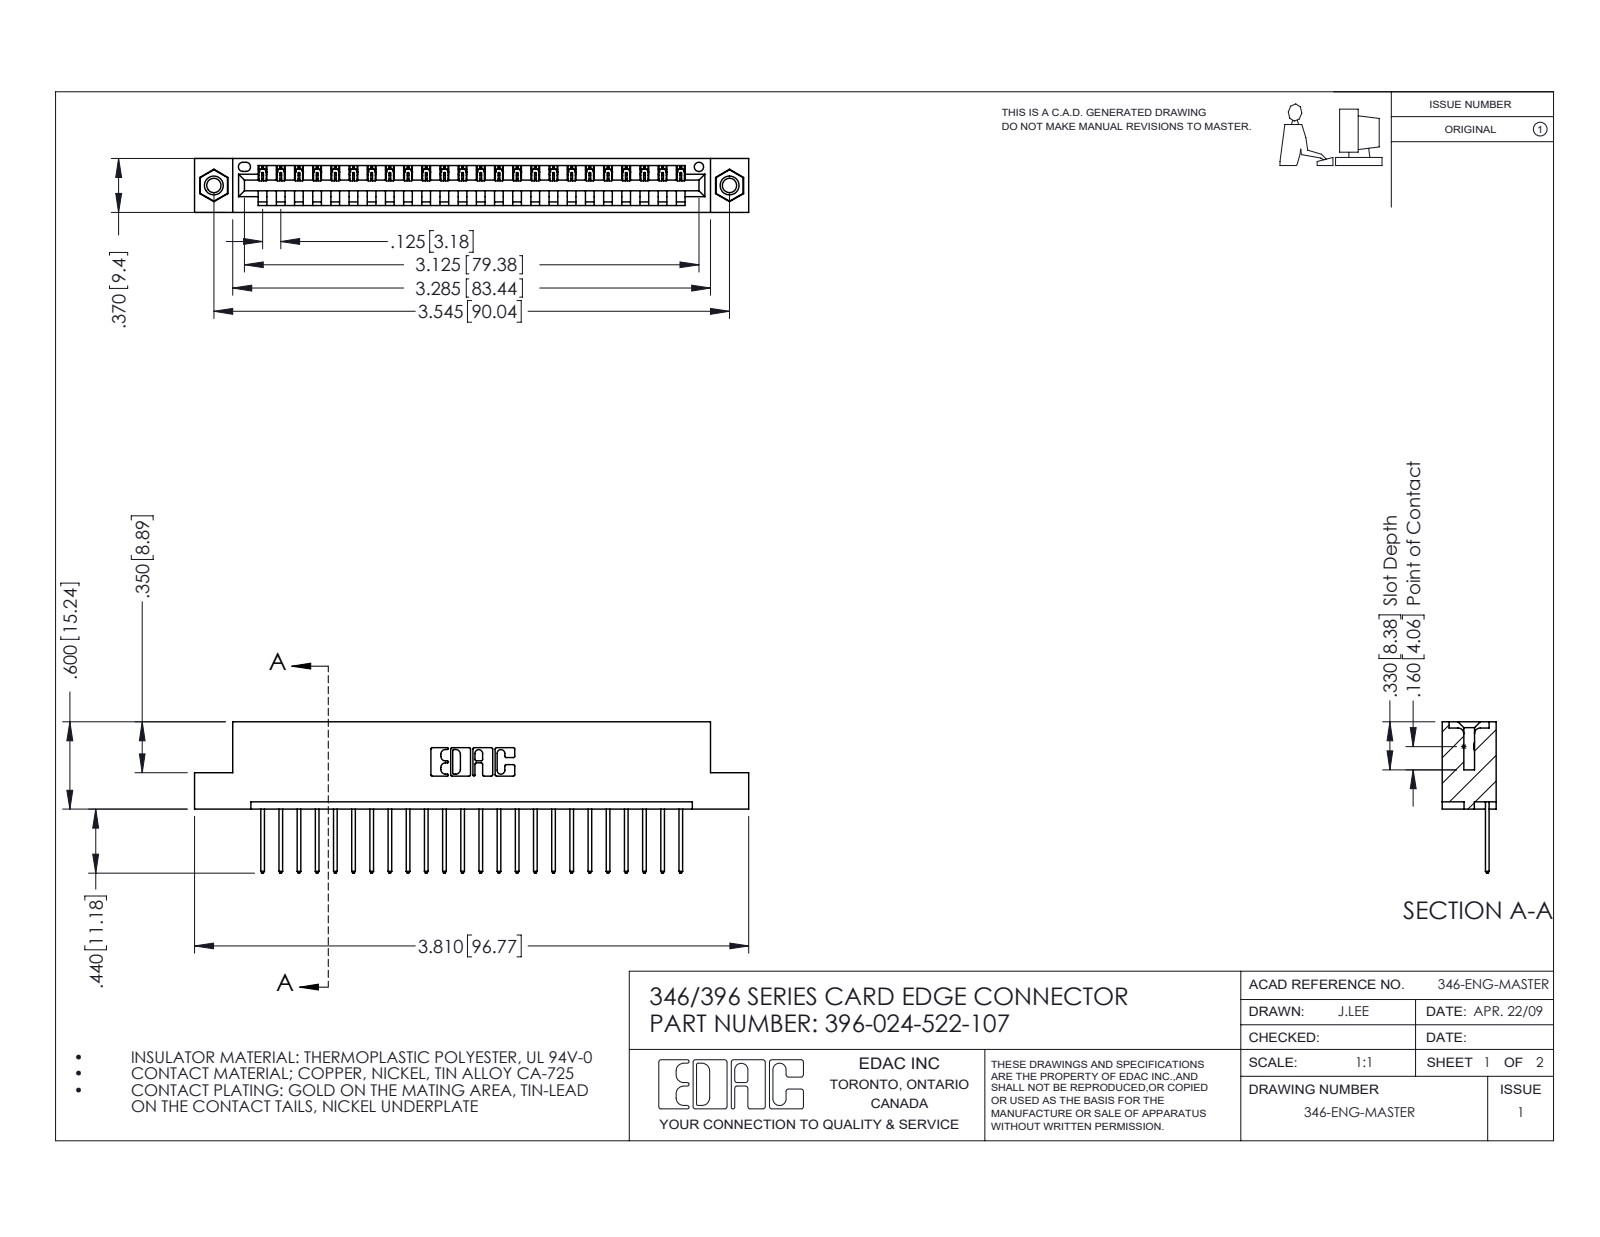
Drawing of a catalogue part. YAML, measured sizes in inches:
part_name: "345-250-001_345-250-005-103; 345-292-001_345-293-122; 396-024-522-107; 346 Part_Flush Mounting Lugs - 0.156 Dia-TI"
step_written_by: "SolidWorks 2016 (CONFIG_CONTROL_DESIGN)"
units: inches
bodies: {solids: 27, faces: 1574, planar: 1068, cylindrical: 490, other: 16}
overall_size: [3.81, 1.04, 0.37]
volume: 0.557
surface_area: 17.57
round_holes:
  - {diameter: 0.098, count: 2}
  - {diameter: 0.125, count: 2}
  - {diameter: 0.156, count: 2}
  - {diameter: 0.064, count: 1}
round_bosses_or_shafts:
  - {diameter: 0.155, count: 2}
partial_cylinders:
  - {radius: 0.006, count: 48}
  - {radius: 0.01, count: 48}
  - {radius: 0.01, count: 22}
  - {radius: 0.007, count: 6}
  - {radius: 0.031, count: 6}
  - {radius: 0.026, count: 3}
  - {radius: 0.031, count: 2}
  - {radius: 0.04, count: 2}
face_to_face_distances: [0.048, 0.322, 0.25, 0.37, 0.072, 0.298, 0.025, 0.148, 0.222, 0.1]
hole_center_spacings: [0.246, 3.337, 3.545]
